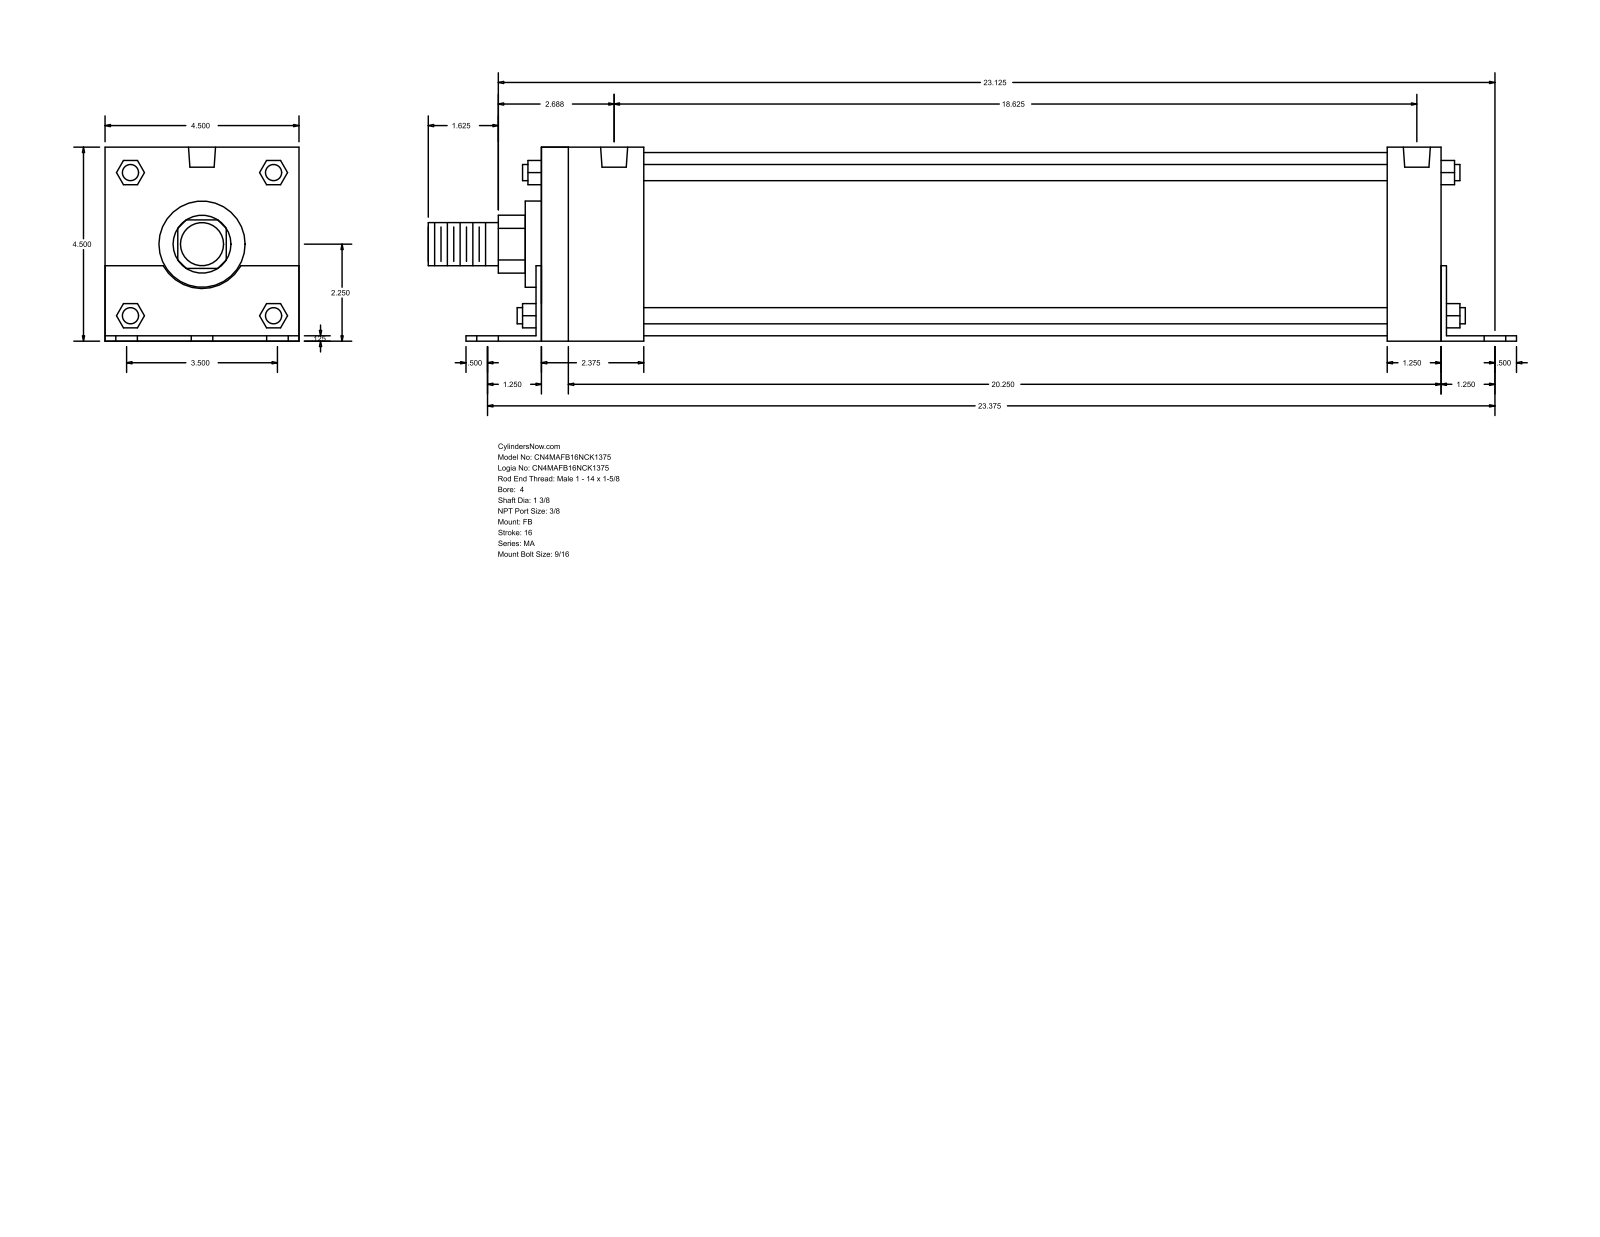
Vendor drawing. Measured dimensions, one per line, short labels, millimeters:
name: MA_FB__0400_1.375
written by: GSSL Pune (CONFIG_CONTROL_DESIGN)
unit: mm
bodies: 0 solids, 140 faces (105 planar, 35 cylindrical, 0 other)
size: 641.35 × 114.35 × 114.3
holes: 6× ⌀14.29, 4× ⌀11.11, 2× ⌀15.93
bosses: 4× ⌀9.53, 1× ⌀107.95, 1× ⌀50.8, 1× ⌀34.92, 1× ⌀25.4
rounds: 1× R17.06, 1× R26.16
face distances: 114.3, 3.17, 114.35, 3.12, 111.18, 530.22, 3.18, 533.4, 533.39, 536.57
hole spacings: 44.45, 595.39, 593.73, 64, 67.5, 86.85, 88.9, 90.98
